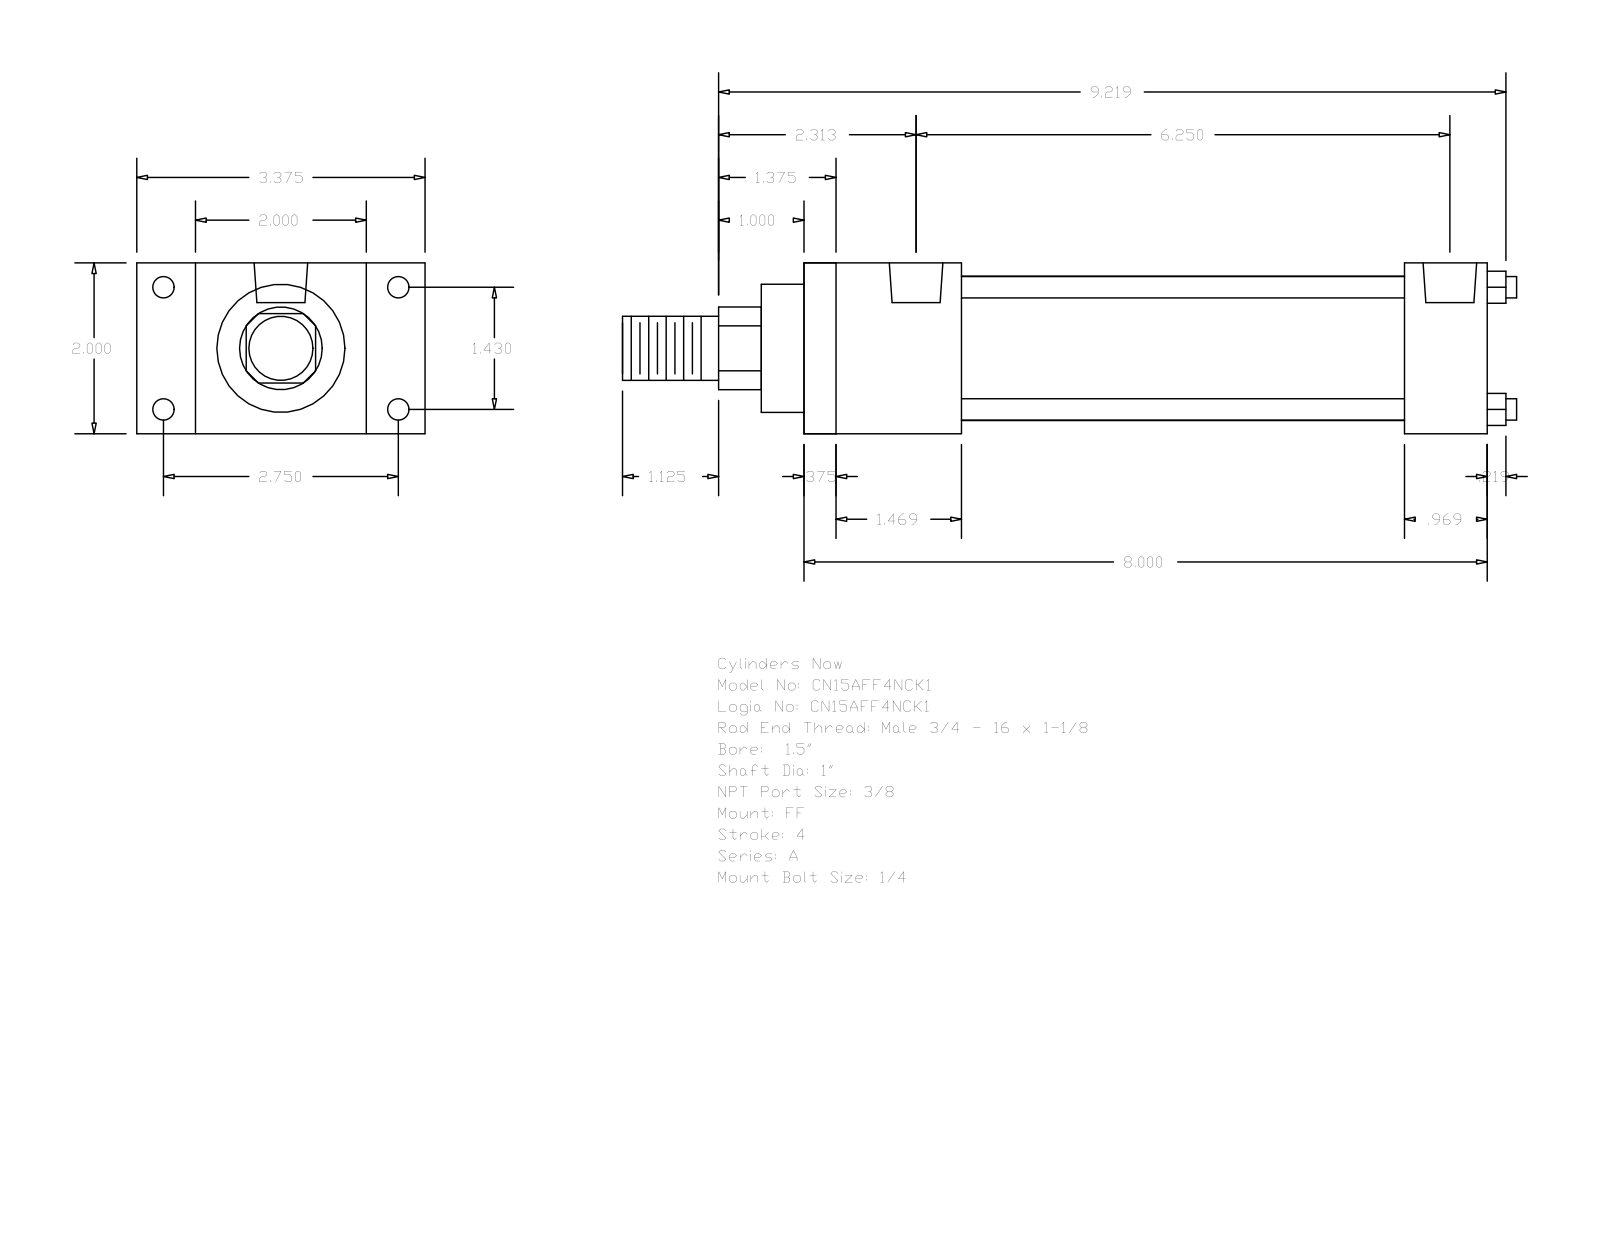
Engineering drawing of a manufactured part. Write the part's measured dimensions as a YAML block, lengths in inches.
part_name: "A_FF__0150_1"
step_written_by: "GSSL Pune (CONFIG_CONTROL_DESIGN)"
units: inches
bodies: {solids: 0, faces: 92, planar: 64, cylindrical: 28, other: 0}
overall_size: [10.469, 3.375, 2]
round_holes:
  - {diameter: 0.219, count: 4}
  - {diameter: 0.25, count: 4}
  - {diameter: 0.627, count: 2}
round_bosses_or_shafts:
  - {diameter: 0.25, count: 4}
  - {diameter: 1.69, count: 1}
  - {diameter: 1.5, count: 1}
  - {diameter: 1, count: 1}
  - {diameter: 0.75, count: 1}
partial_cylinders:
  - {radius: 0.484, count: 1}
face_to_face_distances: [2, 8, 0.375, 7.625, 1.844, 7.031, 1.469, 6.656, 5.187, 6.156]
hole_center_spacings: [0.156, 1.43, 2.75, 3.099, 5.937, 6.094, 6.25]
